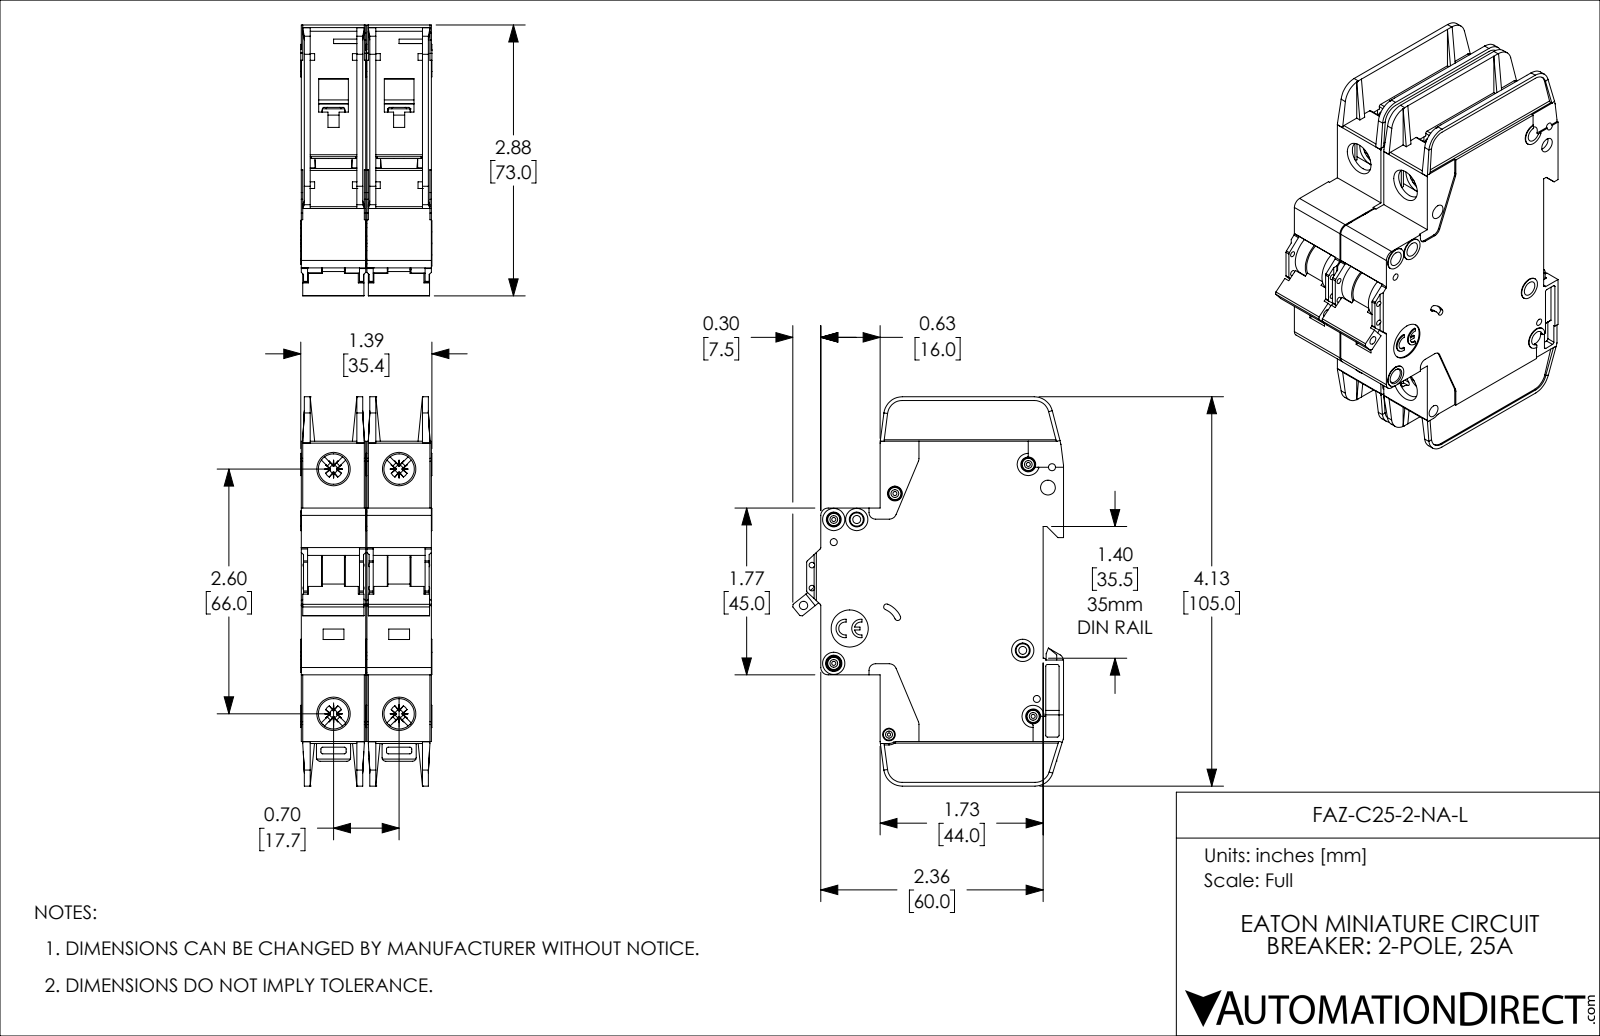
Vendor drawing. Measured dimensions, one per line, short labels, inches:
name: FAZ-C25-2-NA-L
written by: SolidWorks 2019 (AUTOMOTIVE_DESIGN)
unit: in
bodies: 2 solids, 2254 faces (1342 planar, 714 cylindrical, 198 other)
size: 4.134 × 2.876 × 1.394
volume: 9.365 in³; area: 82.01 in²
holes: 8× ⌀0.157, 5× ⌀0.043, 4× ⌀0.075, 4× ⌀0.323, 2× ⌀0.059, 2× ⌀0.085, 1× ⌀0.035, 1× ⌀0.089, 1× ⌀0.098, 1× ⌀0.134, 1× ⌀0.394
bosses: 5× ⌀0.13, 4× ⌀0.236, 3× ⌀0.118, 2× ⌀0.098
rounds: 57× R0.02, 20× R0.016, 14× R0.039, 10× R0.079, 8× R0.043, 5× R0.008, 5× R0.197, 4× R0.01
face distances: 0.697, 0.047, 0.685, 0.591, 0.094, 0.638, 0.543, 1.382, 0.744, 0.65
hole spacings: 0.244, 0.537, 0.697, 0.87, 2.598, 2.69, 0.189, 0.199
